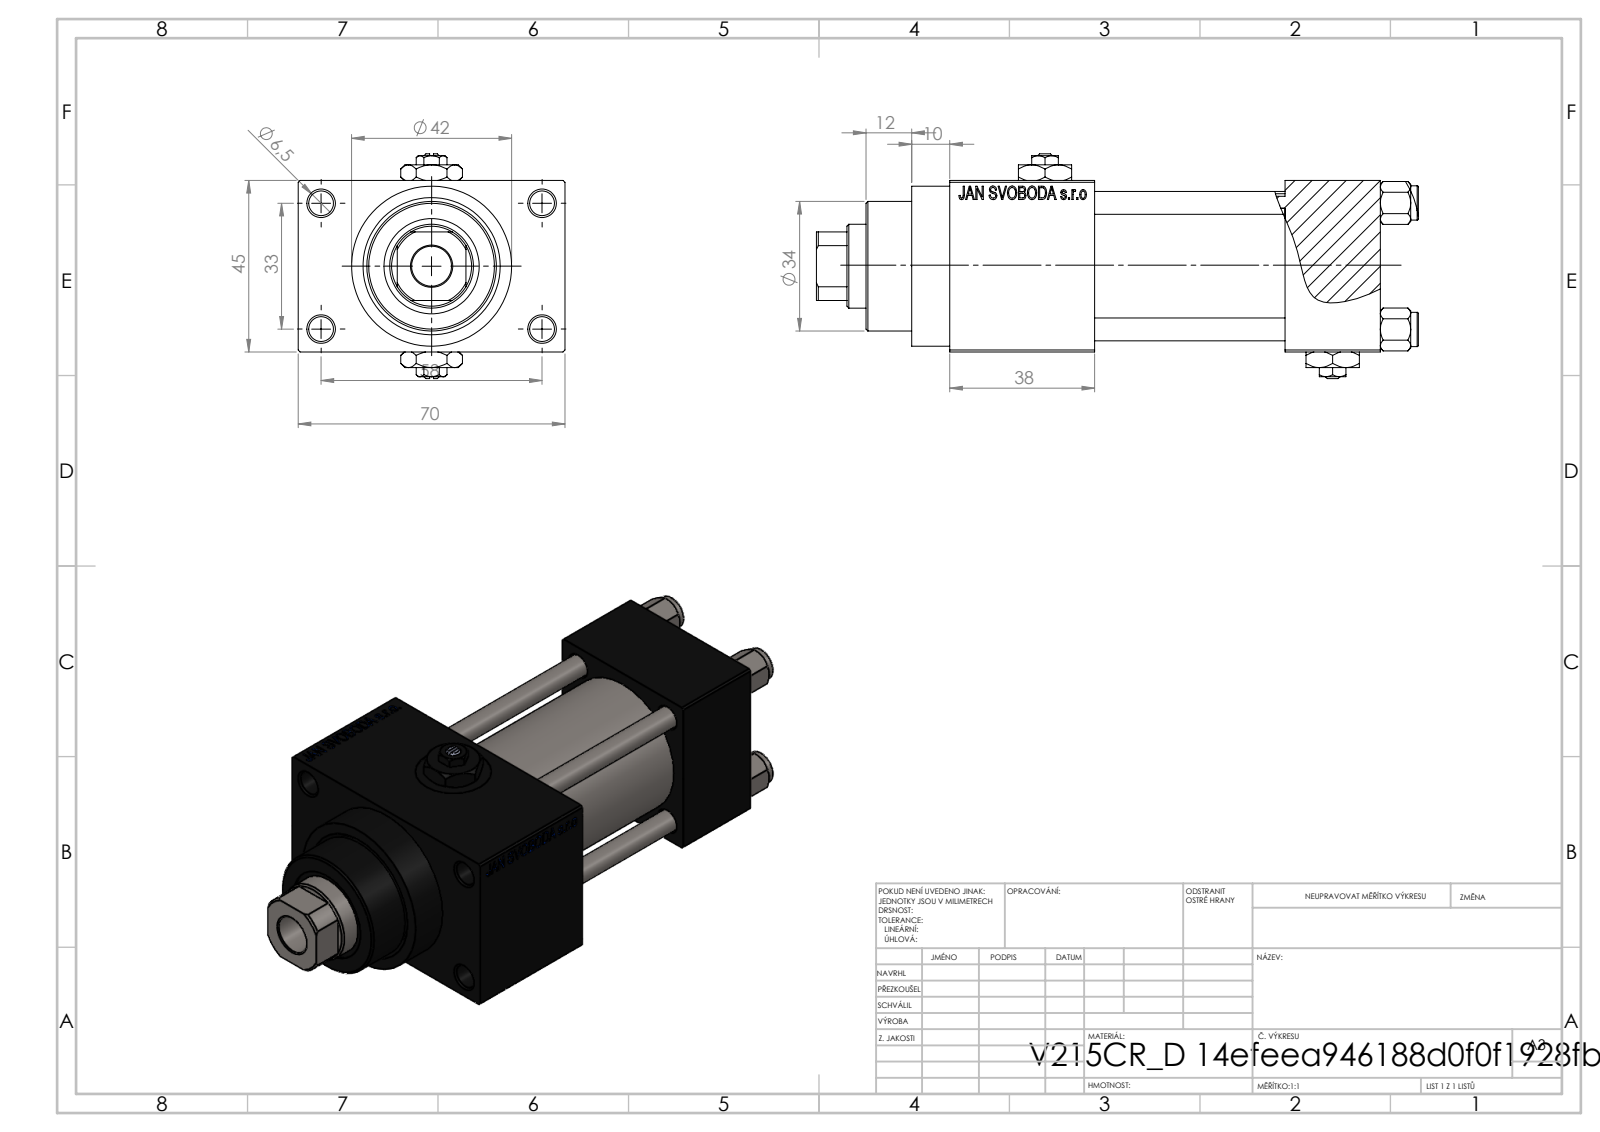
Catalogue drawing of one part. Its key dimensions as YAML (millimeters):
part_name: "NUT_M5_D; Zatka_pro_OIL_PORT; V215CR_D_Body; V215CR_D_TYCINKA (+2 more)"
step_written_by: "SolidWorks 2019 (CONFIG_CONTROL_DESIGN)"
units: millimeters
bodies: {solids: 13, faces: 1189, planar: 540, cylindrical: 89, other: 560}
overall_size: [158, 70, 59]
volume: 246146
surface_area: 80557
round_holes:
  - {diameter: 6, count: 4}
  - {diameter: 6.5, count: 4}
  - {diameter: 7, count: 2}
  - {diameter: 13.16, count: 2}
  - {diameter: 20, count: 2}
  - {diameter: 10.5, count: 1}
  - {diameter: 22, count: 1}
  - {diameter: 24, count: 1}
  - {diameter: 25, count: 1}
  - {diameter: 32, count: 1}
  - {diameter: 33, count: 1}
round_bosses_or_shafts:
  - {diameter: 9, count: 4}
  - {diameter: 42, count: 1}
  - {diameter: 38, count: 1}
  - {diameter: 34, count: 1}
partial_cylinders:
  - {radius: 10.5, count: 1}
face_to_face_distances: [45, 25, 12.5, 57.5, 50, 75, 88, 70, 38, 113]
hole_center_spacings: [12.4, 23.48, 33.2, 33.37, 35.35, 45.6, 56.35, 33]
